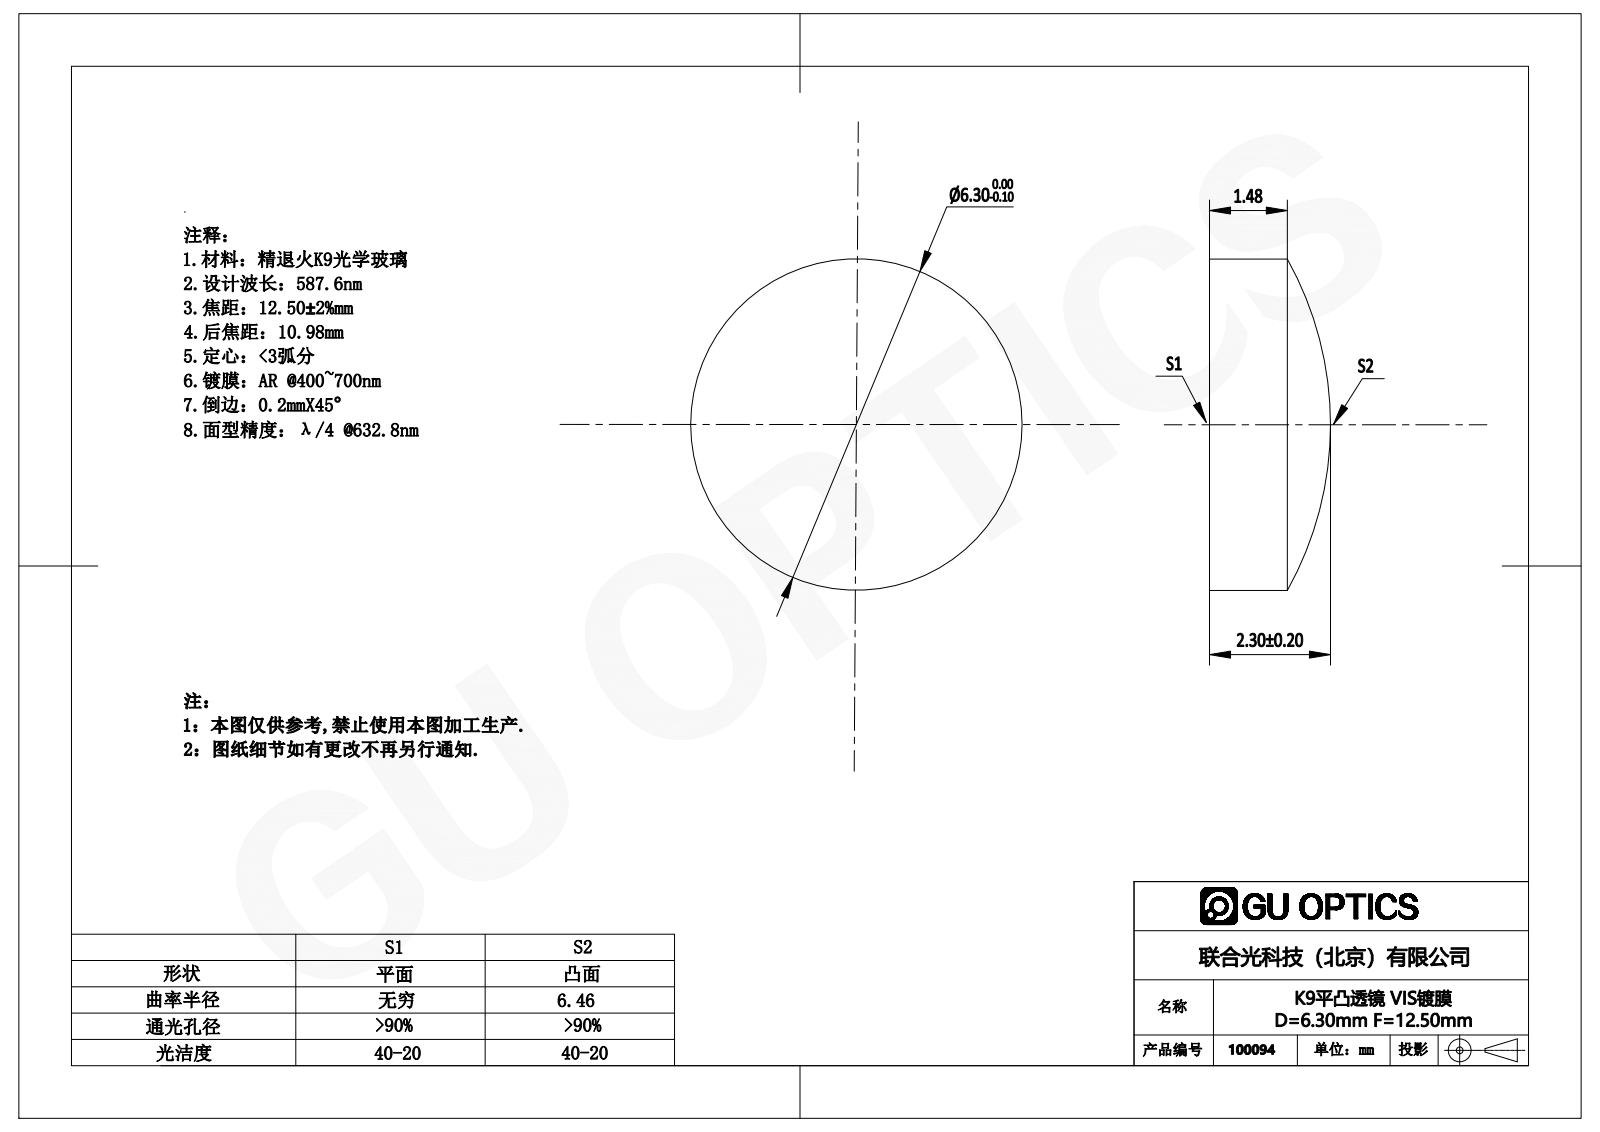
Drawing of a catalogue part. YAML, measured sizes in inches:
part_name: "100094"
step_written_by: "SolidWorks 2016 (AUTOMOTIVE_DESIGN)"
units: inches
bodies: {solids: 1, faces: 5, planar: 1, cylindrical: 2, other: 2}
overall_size: [0.248, 0.248, 0.091]
volume: 0.004
surface_area: 0.15
round_bosses_or_shafts:
  - {diameter: 0.248, count: 1}
